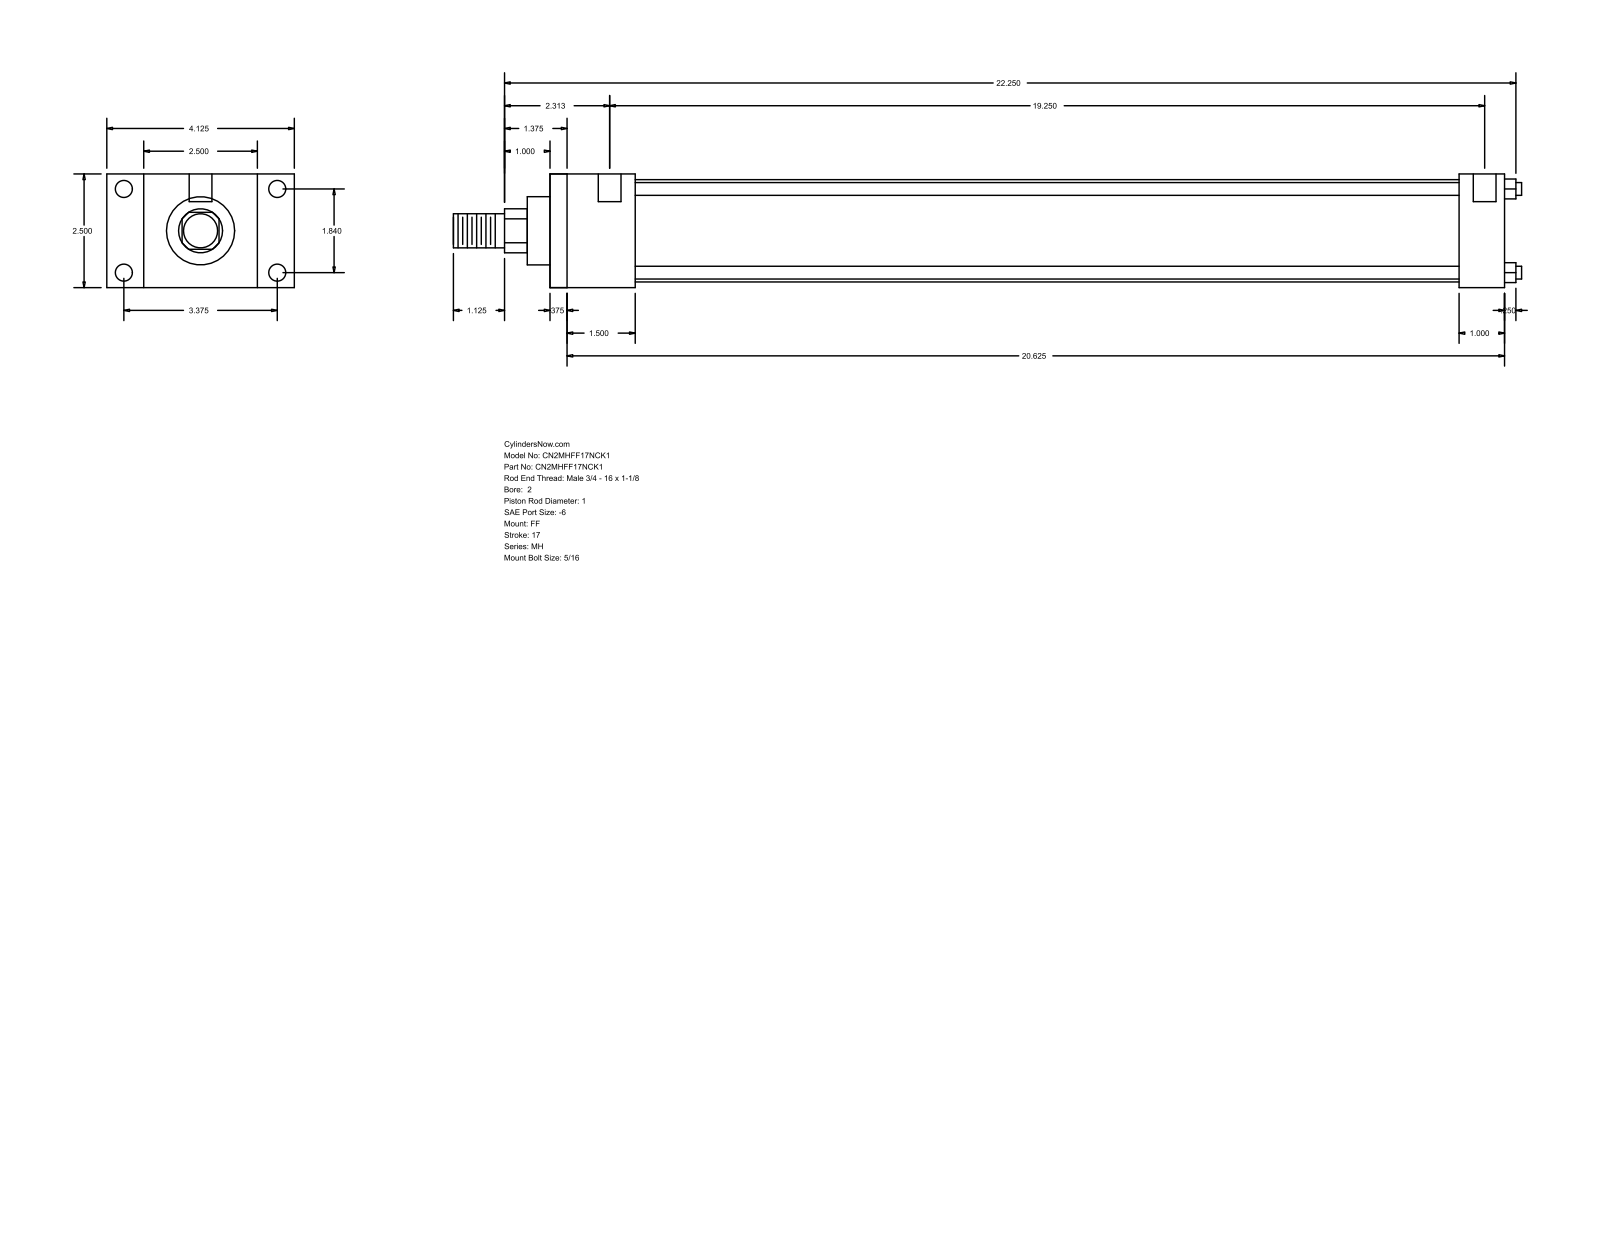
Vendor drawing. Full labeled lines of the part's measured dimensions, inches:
Part name (STEP PRODUCT): MH_FF__0200_1
STEP written by: GSSL Pune (CONFIG_CONTROL_DESIGN)
Units: inches
Bodies: 0 solids, 92 faces (64 planar, 28 cylindrical, 0 other)
Overall size (bounding box): 23.5 × 4.125 × 2.5
Round holes (diameter × count): ⌀0.219 ×4, ⌀0.375 ×4, ⌀0.5 ×2
Round bosses / shafts (diameter × count): ⌀0.281 ×4, ⌀2.25 ×1, ⌀1.5 ×1, ⌀1 ×1, ⌀0.75 ×1
Partial cylindrical surfaces — rounded edges, fillets, slot ends (radius × count): R0.484 ×1
Main face-to-face distances: 2.5, 21, 0.375, 20.625, 0.813, 1, 1.875, 20, 1.5, 19.625
Hole centre spacings: 1.84, 3.375, 3.844, 19.562, 0.125, 0.187, 19.25, 19.375
